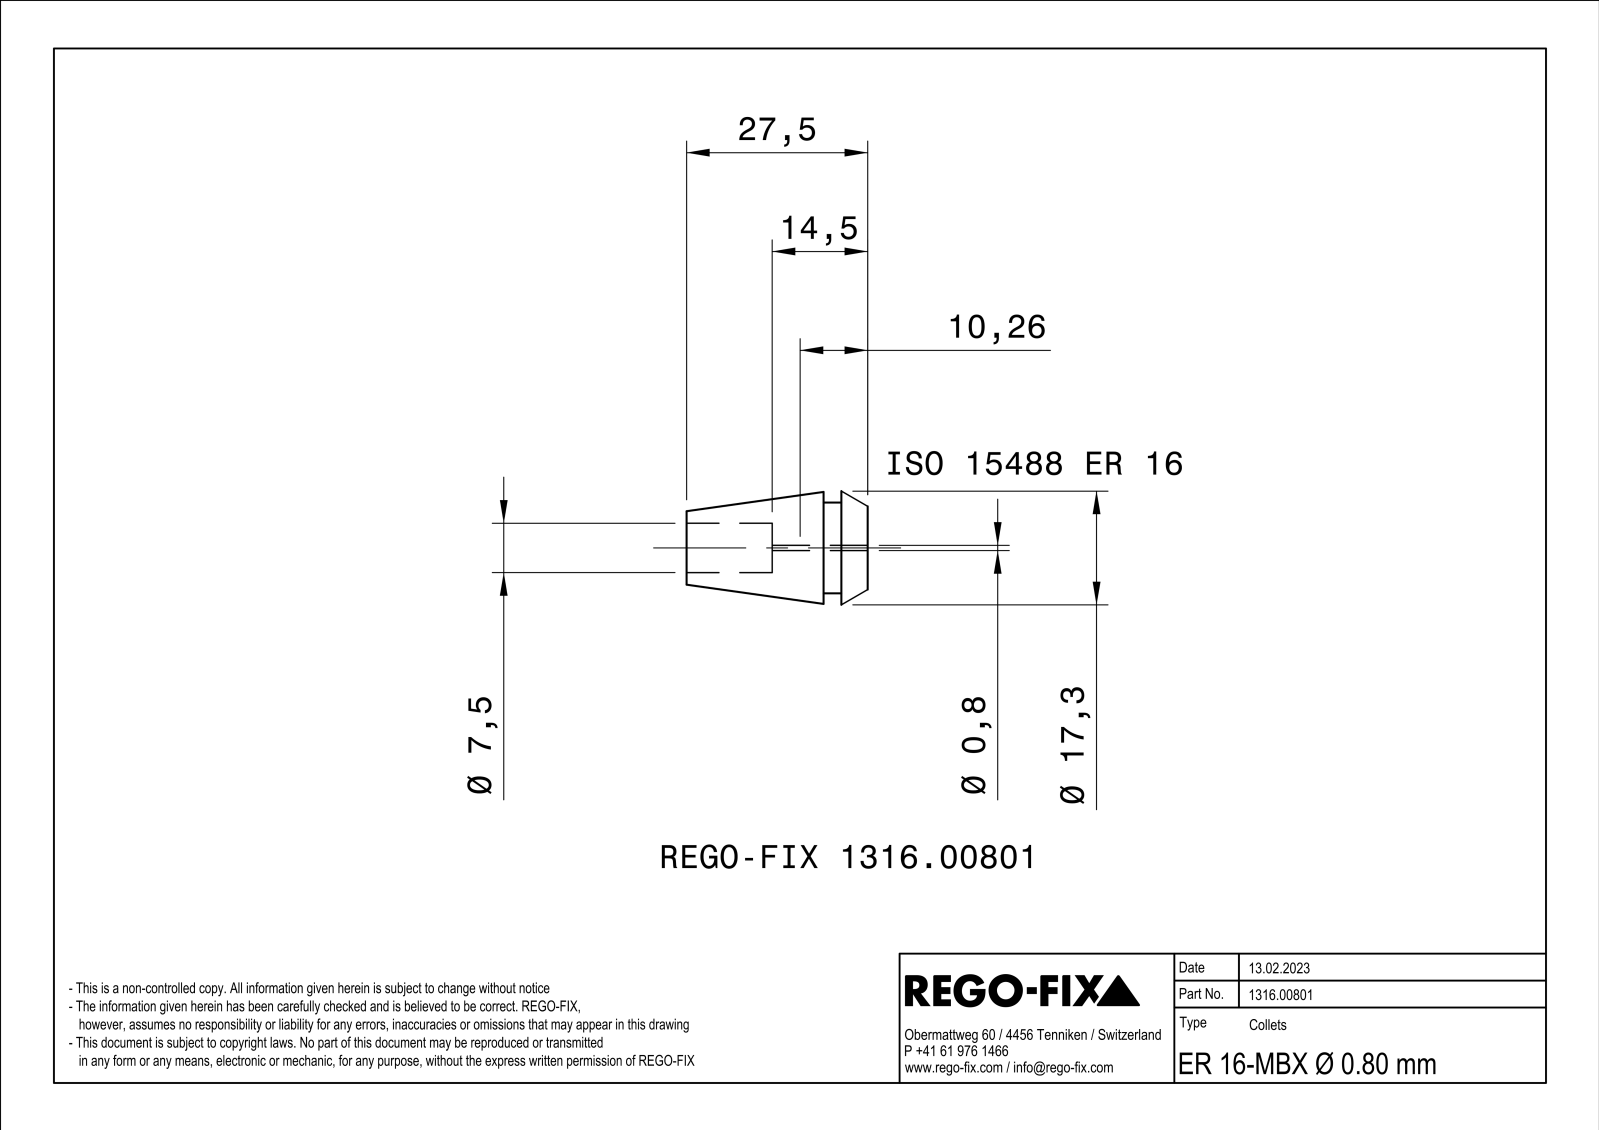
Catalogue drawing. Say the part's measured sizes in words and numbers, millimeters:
The part is named "NOCUT". Its 3-D file was written by "SIEMENS PLM Software Solid Edge ST10 (AUTOMOTIVE_DESIGN)". It is 1 solid with 109 faces: 36 planar, 27 cylindrical and 46 other. Overall it measures 27.5 by 16.91 by 16.9 millimeters. Its volume is 3 301 cubic millimeters and its surface area 3 318 square millimeters. Round holes: 3 of diameter 2, 1 of diameter 7.5. Round bosses or shafts: 1 of diameter 13.8. Partial cylindrical surfaces (rounded edges, fillets, slot ends): 3 of radius 0.14, 3 of radius 25, 1 of radius 0.4. The main face-to-face distances are 0.54, 0.8, 6.7, 4, 2.7, 27.5, 23.5, 20.8, 14.5, 10.5. The hole center spacings are 2.1, 3.64.
